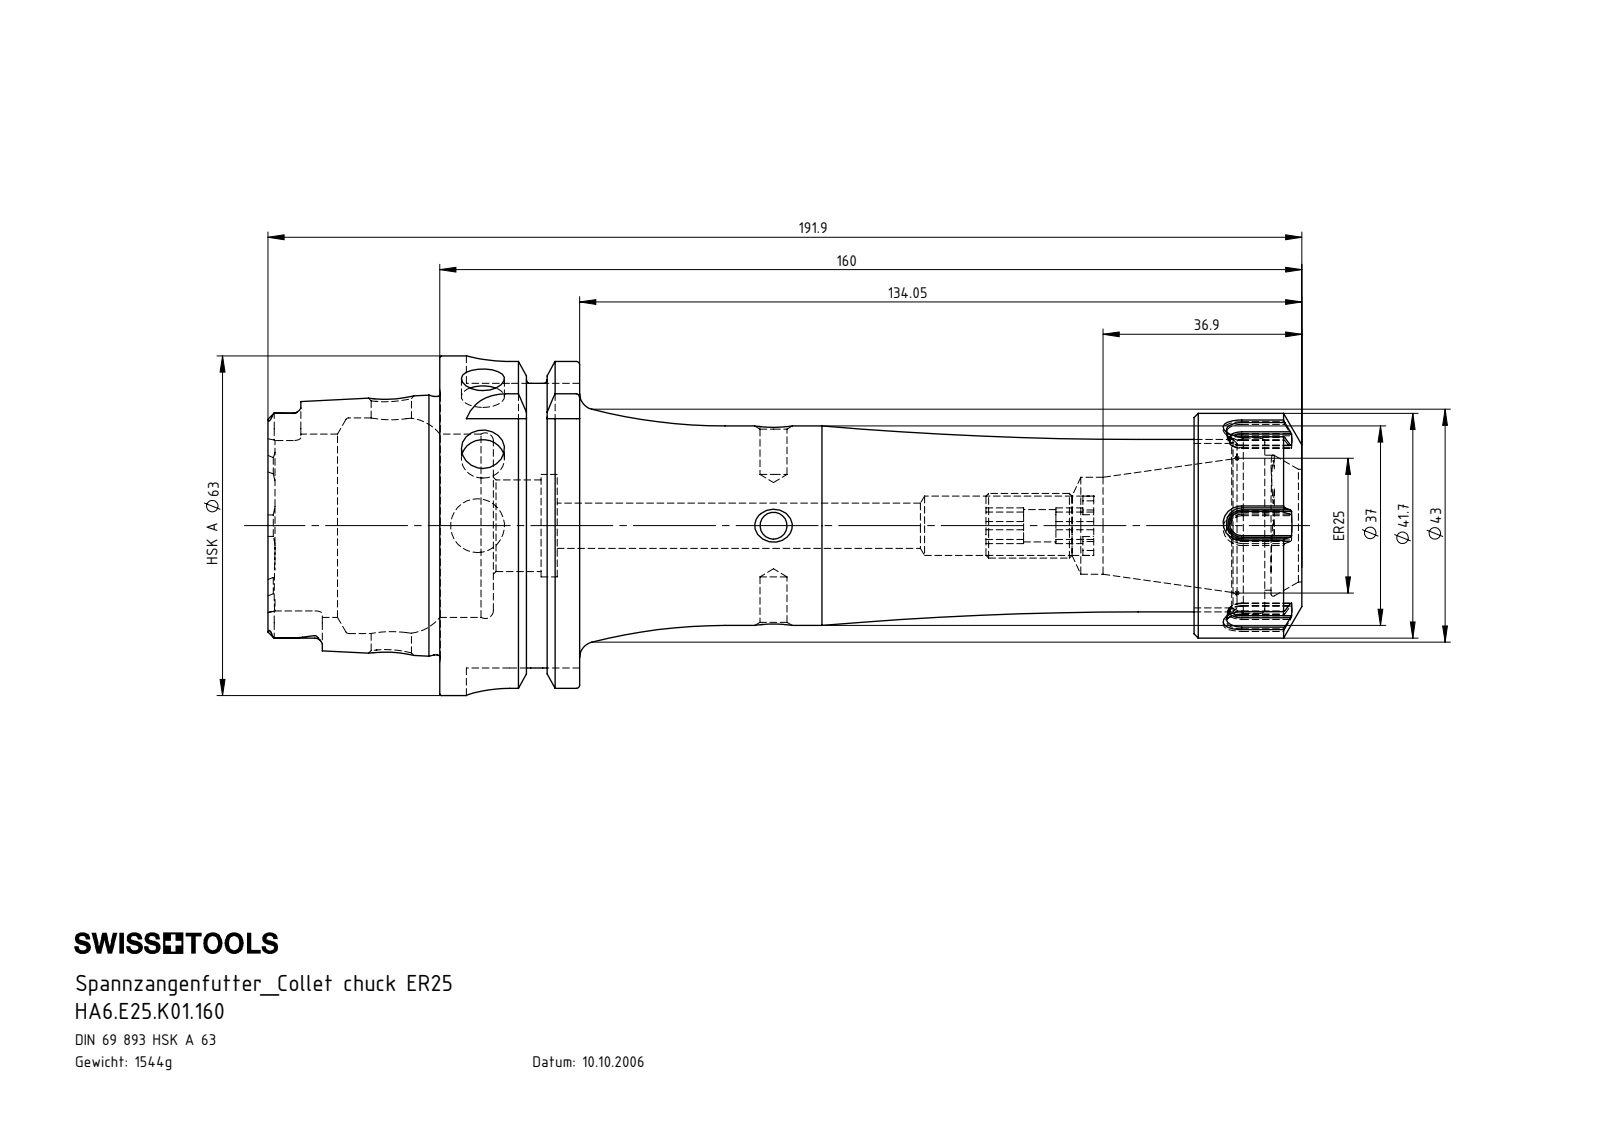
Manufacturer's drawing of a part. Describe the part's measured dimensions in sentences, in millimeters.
The part is named "ERU-AN5.K01.020_A; E25-ER1.001.020; HA6-E25.K01.160_C_Fertigbearbeitung; HA6-E25.K01.160". Its 3-D file was written by "SolidWorks 2012 (CONFIG_CONTROL_DESIGN)". It is 3 solids with 348 faces: 131 planar, 80 cylindrical and 137 other. Overall it measures 191.9 by 63 by 63 millimeters. Its volume is 196 733 cubic millimeters and its surface area 47 522 square millimeters. Round holes: 2 of diameter 5, 2 of diameter 8, 1 of diameter 6, 1 of diameter 7.5, 1 of diameter 8.4, 1 of diameter 10, 1 of diameter 11, 1 of diameter 17, 1 of diameter 18, 1 of diameter 19, 1 of diameter 20.9, 1 of diameter 30.5. Round bosses or shafts: 1 of diameter 63, 1 of diameter 54.95, 1 of diameter 47.94, 1 of diameter 41.7, 1 of diameter 37, 1 of diameter 32, 1 of diameter 12. Partial cylindrical surfaces (rounded edges, fillets, slot ends): 6 of radius 1.4, 4 of radius 2.88, 4 of radius 8, 2 of radius 12.17. The main face-to-face distances are 25.95, 16, 140, 114.05, 9.95, 130.05, 20, 160, 150.05, 134.05. The hole center spacings are 54.95, 70.95.
